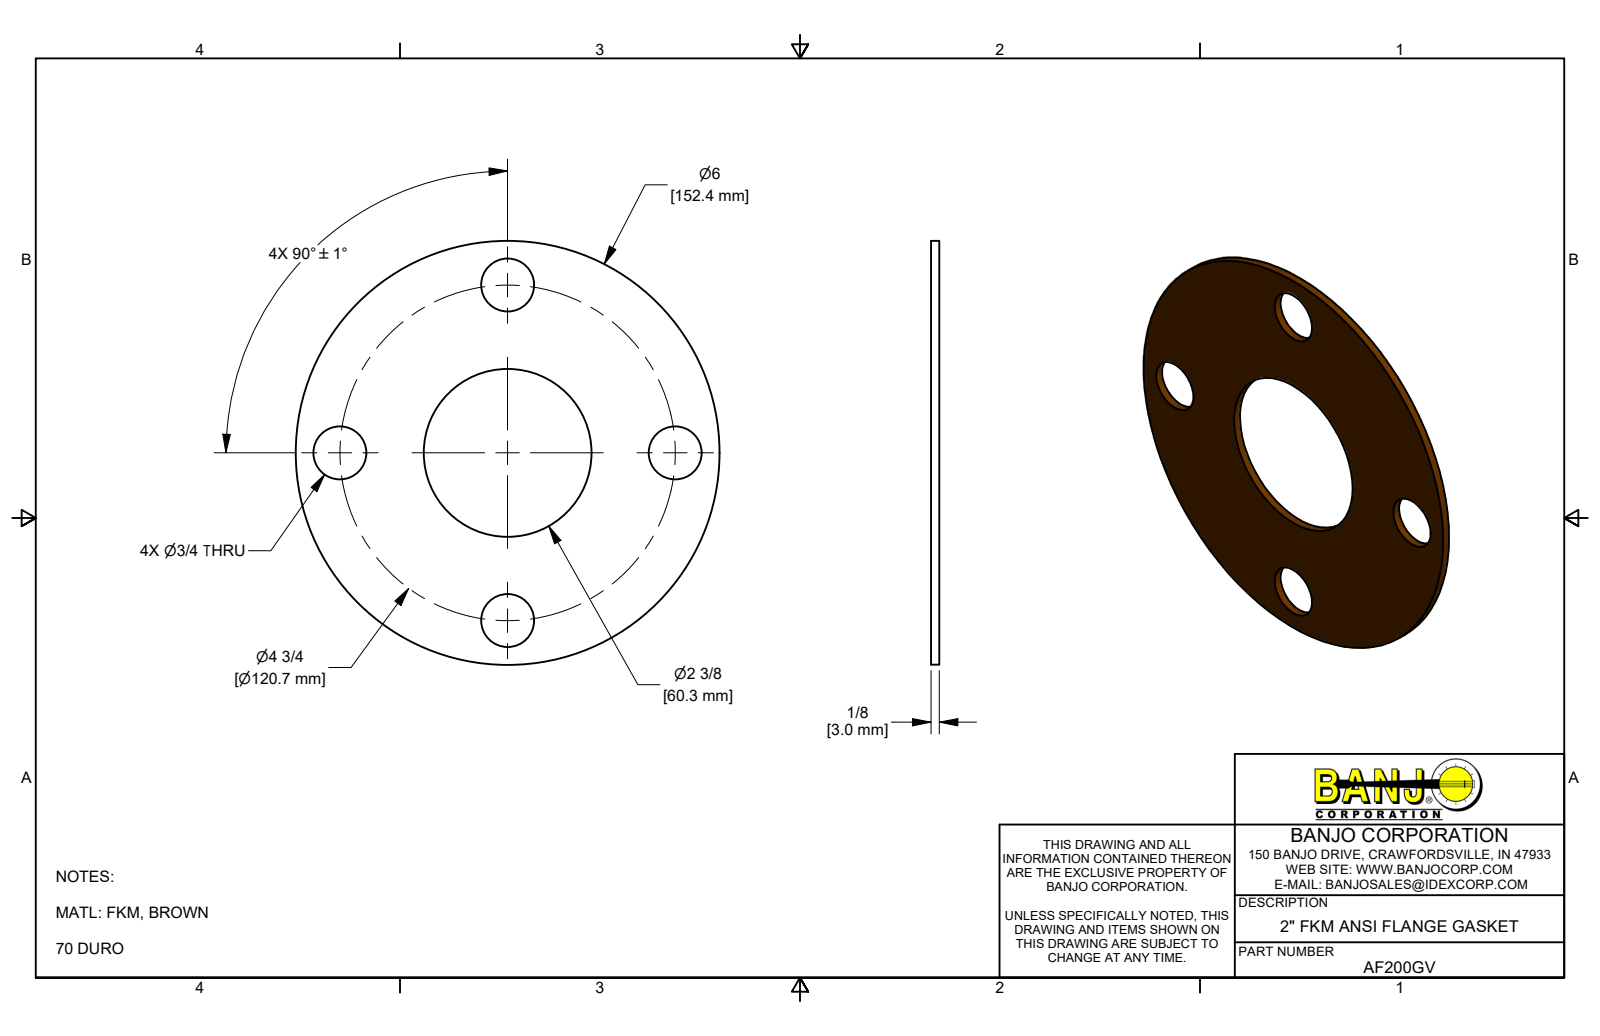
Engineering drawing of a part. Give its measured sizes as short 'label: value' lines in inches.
name: AF200GV
written by: Autodesk Inventor 2019 (AUTOMOTIVE_DESIGN)
unit: in
bodies: 1 solid, 8 faces (2 planar, 6 cylindrical, 0 other)
size: 6 × 6 × 0.118
volume: 2.605 in³; area: 48.37 in²
holes: 4× ⌀0.75, 1× ⌀2.375
bosses: 1× ⌀6
face distances: 0.118
hole spacings: 2.375, 3.359, 4.75
